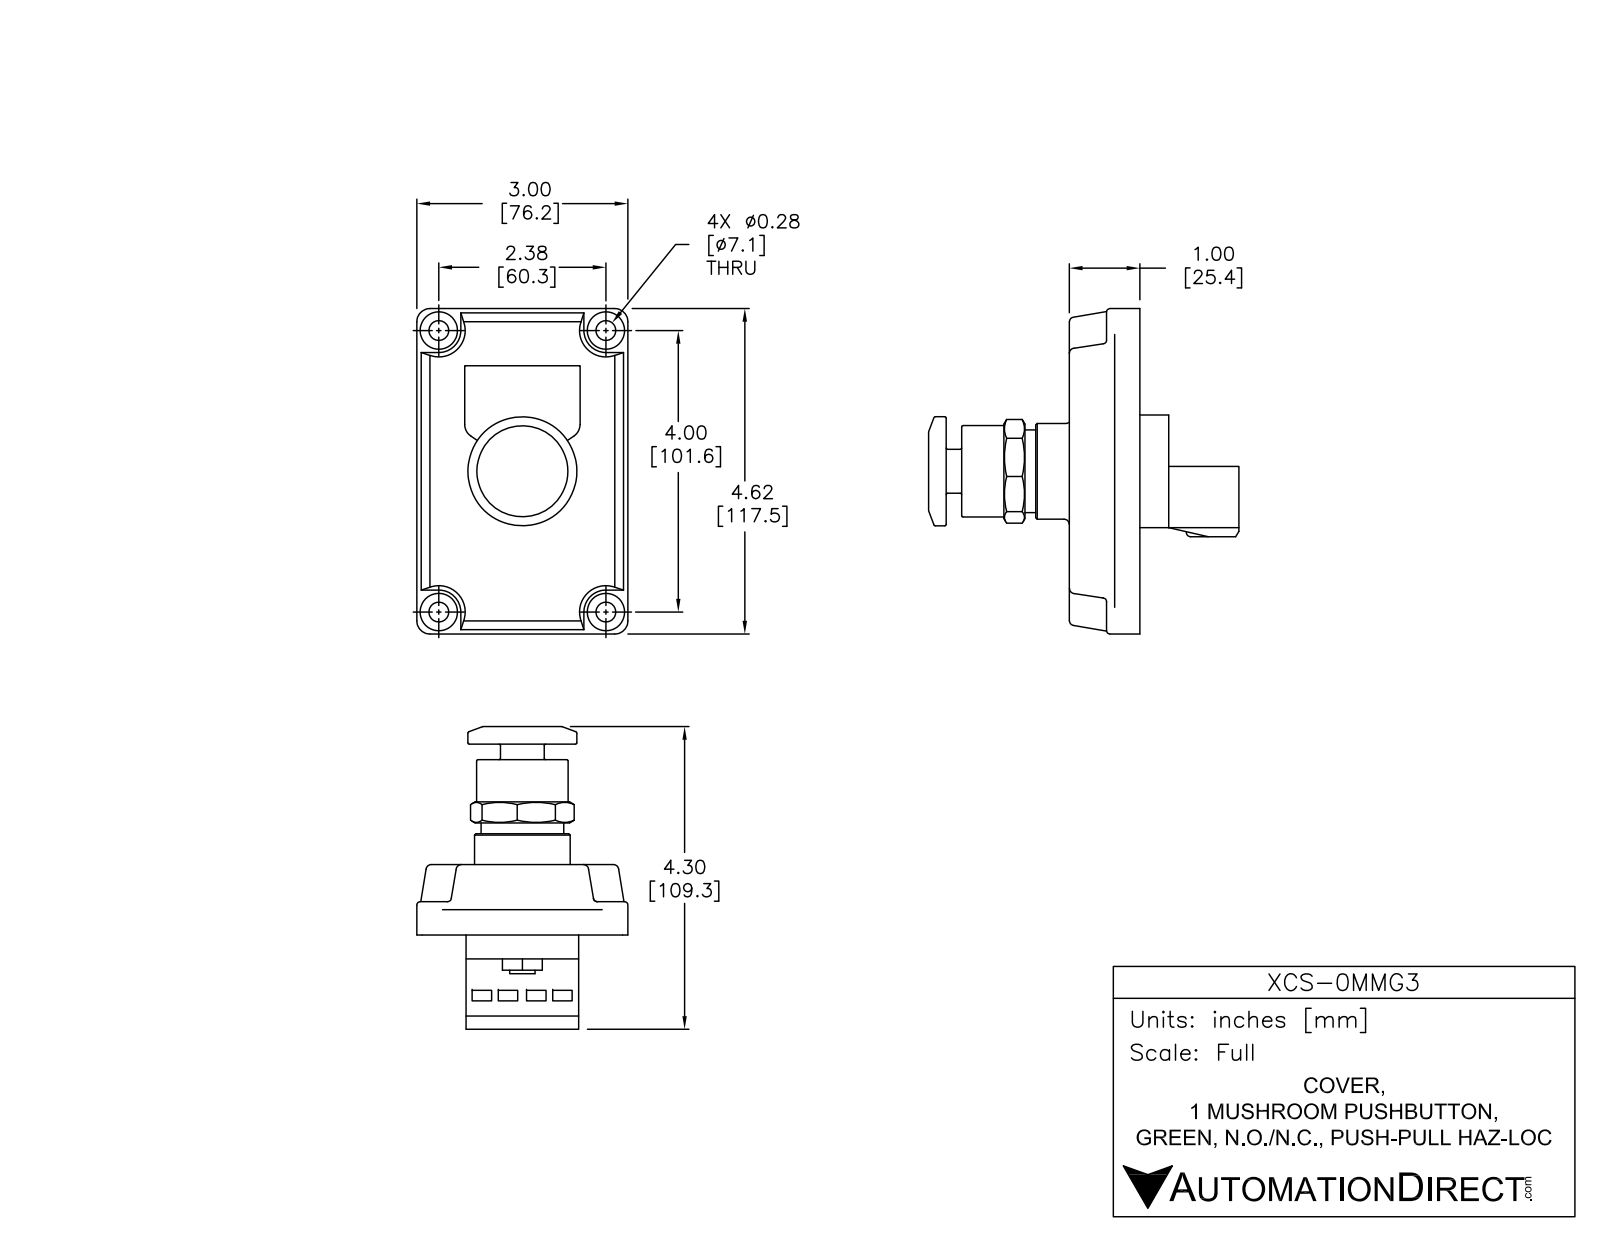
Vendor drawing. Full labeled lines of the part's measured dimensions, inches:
Part name (STEP PRODUCT): XCS-0MMG3
STEP written by: SolidWorks 2015 (AUTOMOTIVE_DESIGN)
Units: inches
Bodies: 4 solids, 333 faces (114 planar, 117 cylindrical, 102 other)
Overall size (bounding box): 4.63 × 3.1 × 3.024
Volume: 11.45 in³ · Surface area: 66.23 in²
Round holes (diameter × count): ⌀0.27 ×4, ⌀1.36 ×1
Round bosses / shafts (diameter × count): ⌀0.13 ×4, ⌀1.55 ×1, ⌀1.3 ×1, ⌀1.175 ×1, ⌀0.623 ×1
Partial cylindrical surfaces — rounded edges, fillets, slot ends (radius × count): R0.01 ×28, R0.02 ×8, R0.055 ×8, R0.05 ×4, R0.1 ×4, R0.38 ×4, R0.8 ×4, R0.4 ×3
Main face-to-face distances: 0.525, 0.5, 1.025, 2.774, 2.274, 1.749, 0.455, 2.585, 0.02, 3.02
Hole centre spacings: 2.327, 2.38, 4, 4.655
